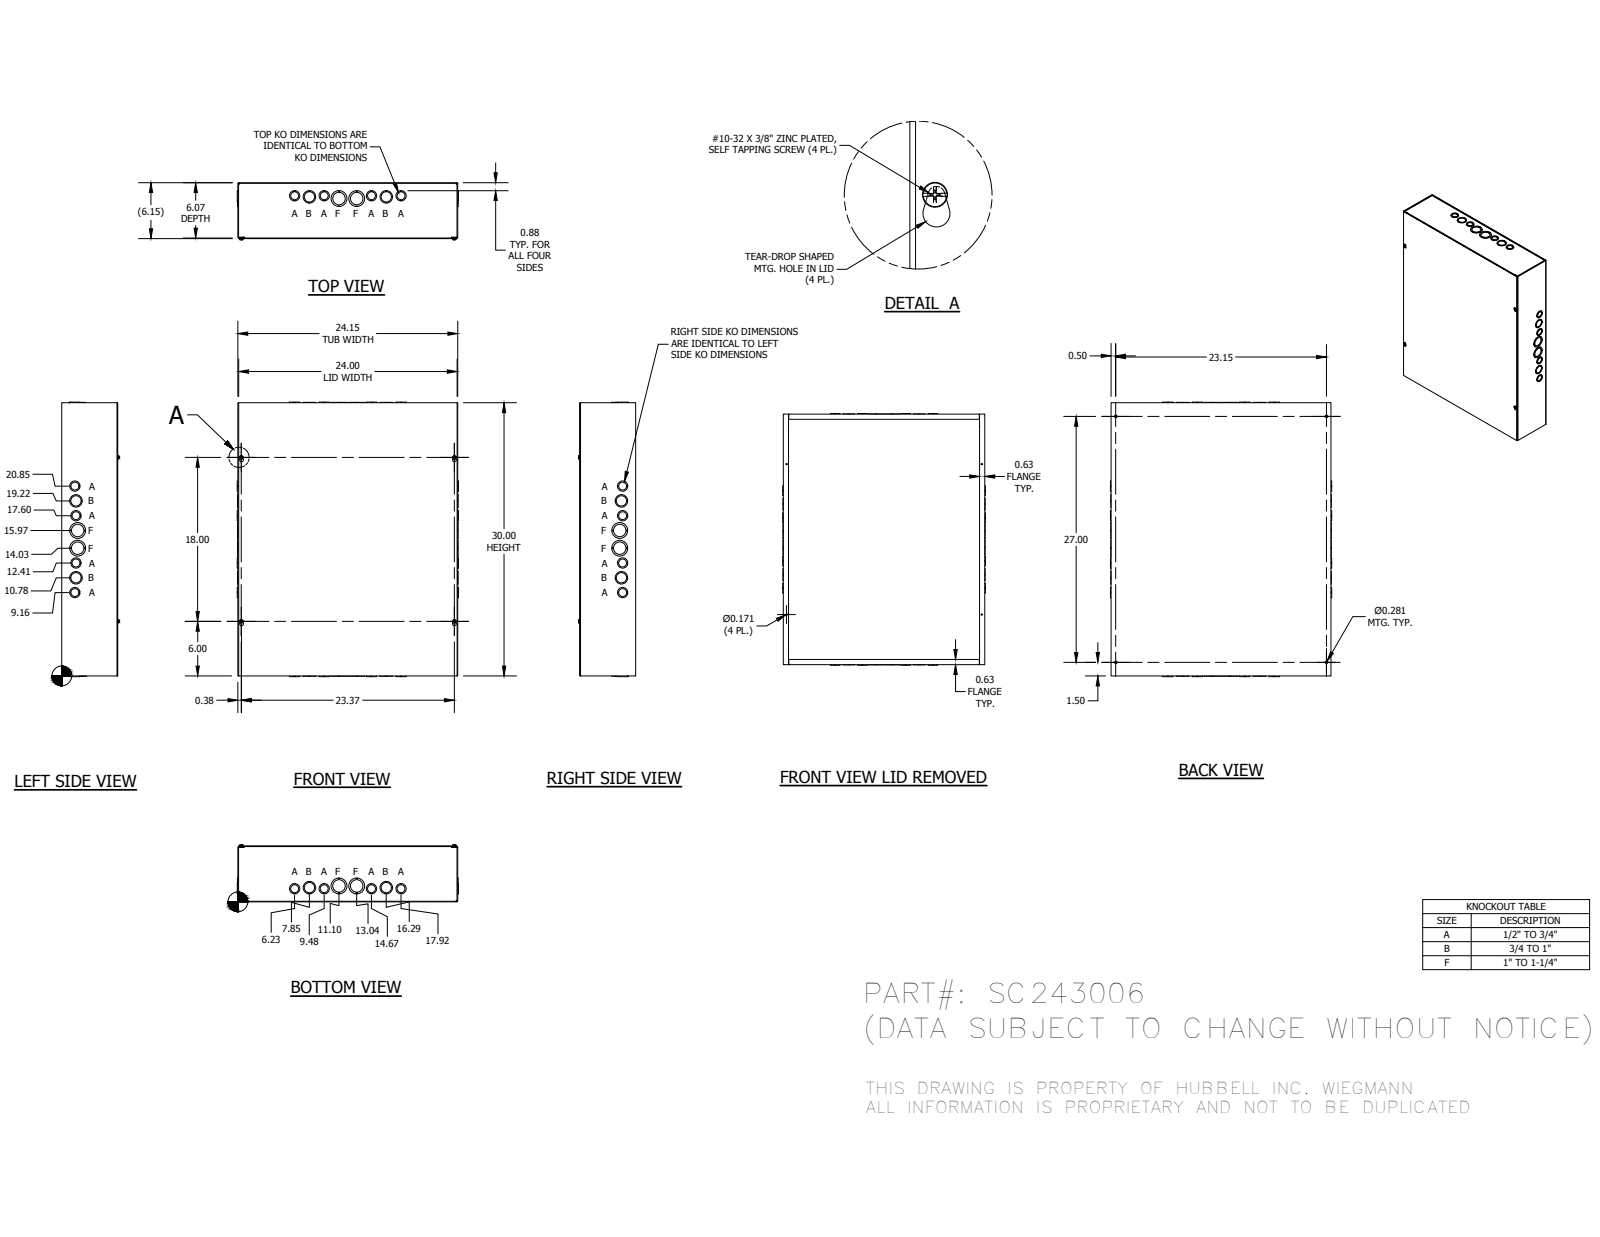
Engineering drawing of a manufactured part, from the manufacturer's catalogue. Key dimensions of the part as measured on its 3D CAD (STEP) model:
Part name (STEP PRODUCT): SC243006BLR; SC2406TB; SC2430LPA; 37214 (+1 more)
STEP written by: Autodesk Inventor 2014 (AUTOMOTIVE_DESIGN)
Units: millimetres
Bodies: 37 solids, 1219 faces (899 planar, 236 cylindrical, 84 other)
Overall size (bounding box): 765.76 × 617.12 × 159.51
Round holes (diameter × count): ⌀28.57 ×14, ⌀22.22 ×10, ⌀34.92 ×8, ⌀4.34 ×4, ⌀7.14 ×4, ⌀44.45 ×4
Round bosses / shafts (diameter × count): ⌀4.83 ×4
Partial cylindrical surfaces — rounded edges, fillets, slot ends (radius × count): R0.4 ×12, R2.28 ×12, R3.17 ×4, R5.16 ×4
Main face-to-face distances: 1.88, 154.28, 152.4, 156.16, 611.48, 760.12, 609.6, 613.36, 762, 758.24
Hole centre spacings: 41.39, 41.4, 42.03, 82.55, 82.69, 90.9, 114.34, 124.07
